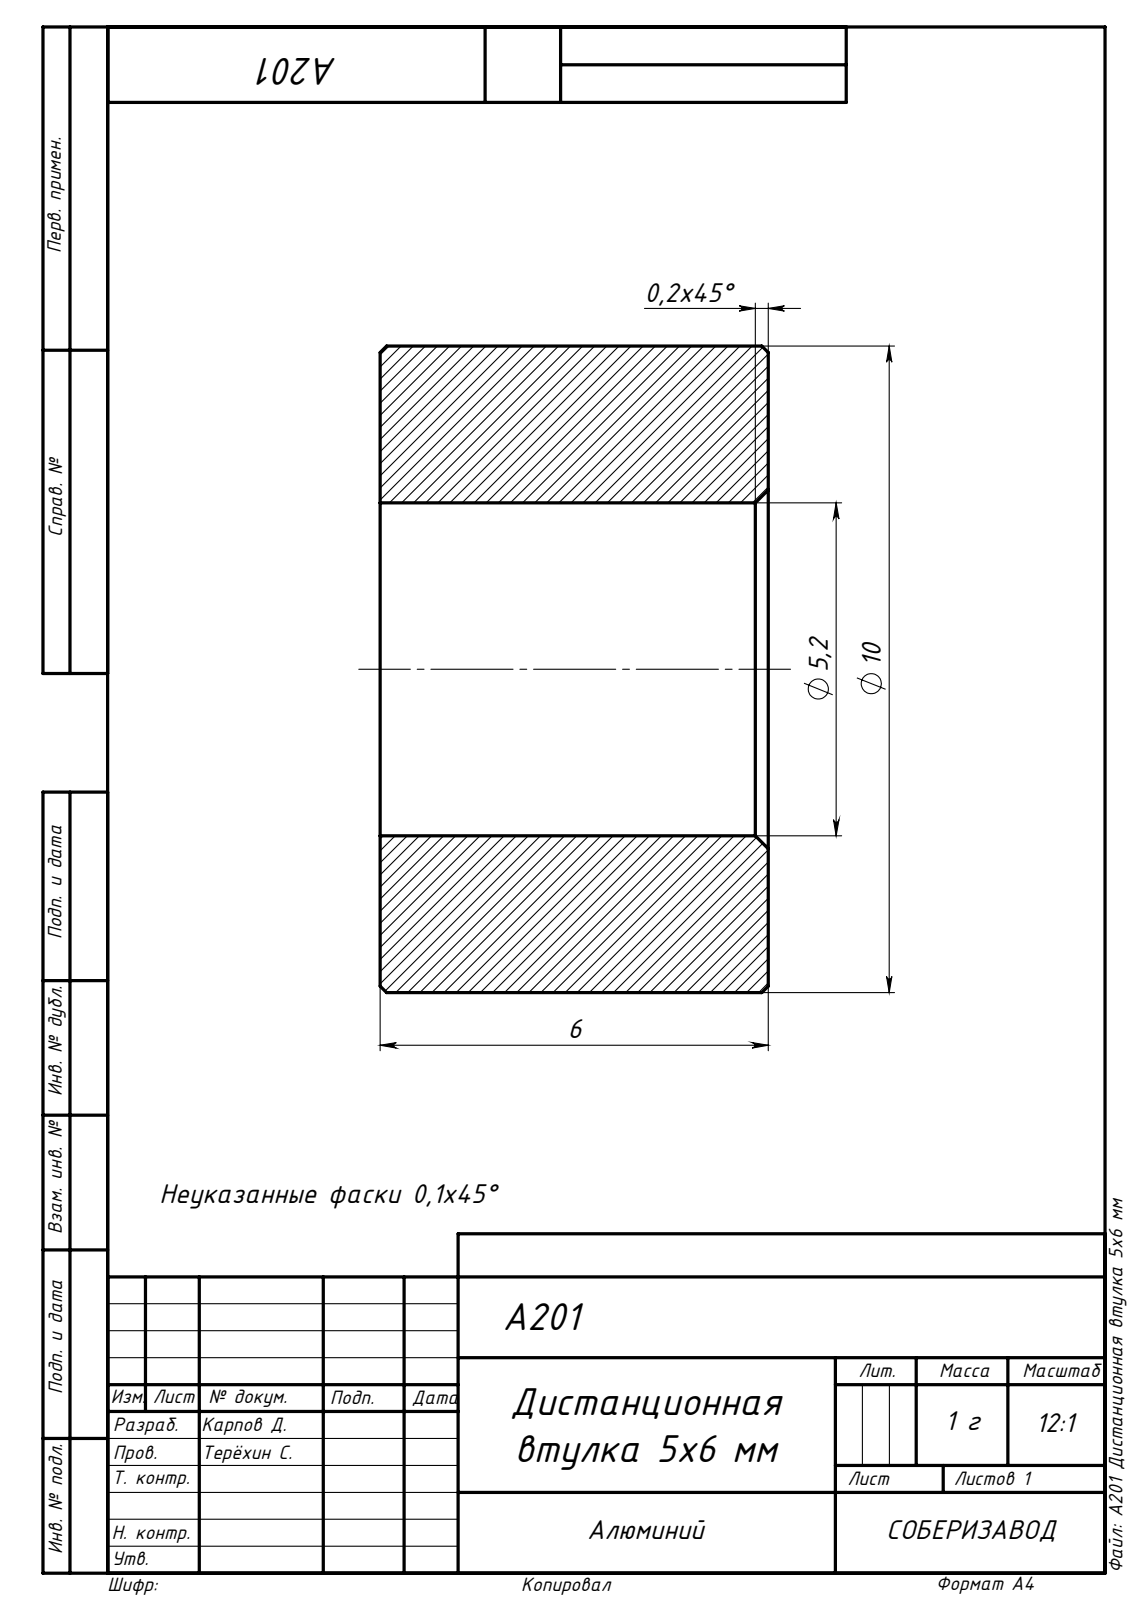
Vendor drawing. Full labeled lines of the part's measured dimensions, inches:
Part name (STEP PRODUCT): A201 Дистанционная втулка 5х6 мм
STEP written by: SolidWorks 2020 (AUTOMOTIVE_DESIGN)
Units: inches
Bodies: 1 solid, 12 faces (2 planar, 4 cylindrical, 6 other)
Overall size (bounding box): 0.394 × 0.394 × 0.236
Volume: 0.021 in³ · Surface area: 0.612 in²
Round holes (diameter × count): ⌀0.203 ×1
Round bosses / shafts (diameter × count): ⌀0.394 ×1
Main face-to-face distances: 0.236
